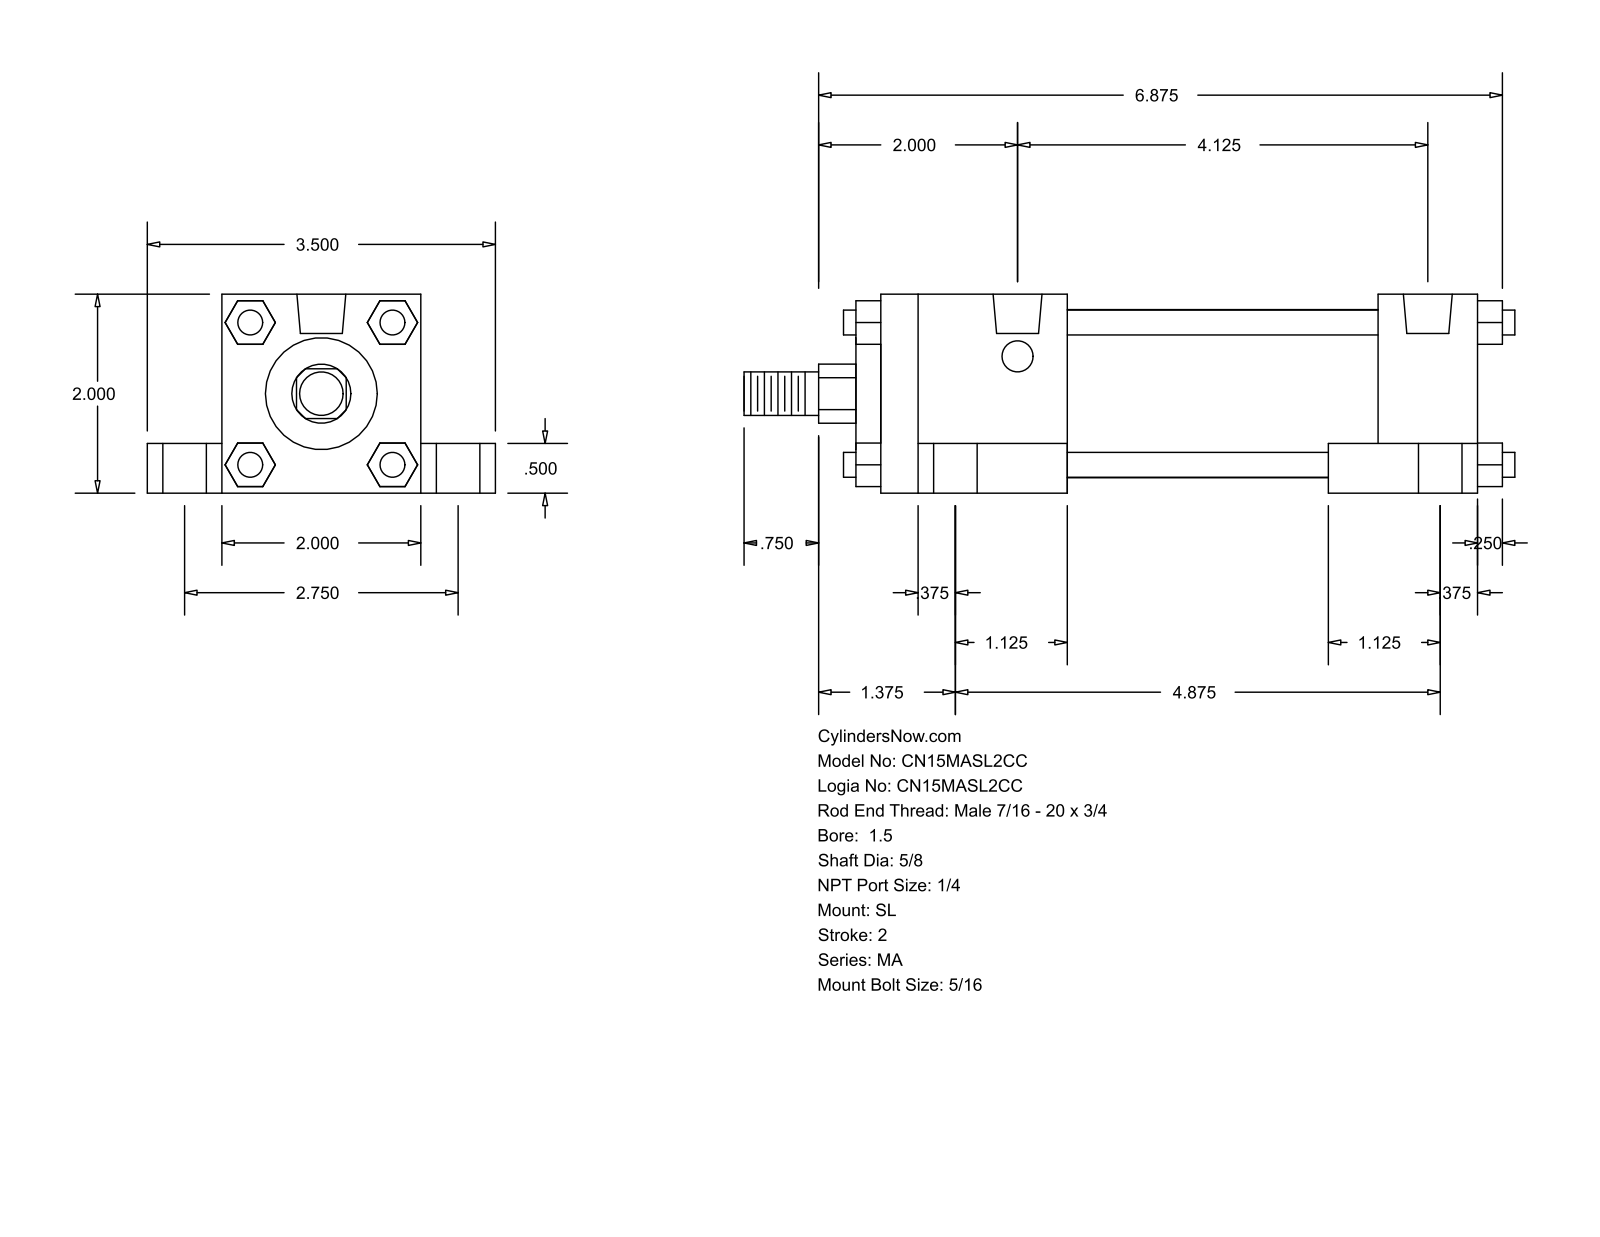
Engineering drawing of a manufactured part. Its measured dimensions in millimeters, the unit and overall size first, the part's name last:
Units: millimetres
Overall size (bounding box): 196.85 × 88.9 × 50.8
Round holes (diameter × count): ⌀7.94 ×4, ⌀11.11 ×4, ⌀17.46 ×4, ⌀12.49 ×2
Round bosses / shafts (diameter × count): ⌀6.35 ×4, ⌀42.93 ×1, ⌀28.57 ×1, ⌀15.88 ×1, ⌀11.11 ×1
Partial cylindrical surfaces — rounded edges, fillets, slot ends (radius × count): R7.54 ×1
Main face-to-face distances: 50.8, 19.05, 38.1, 152.4, 69.85, 12.7, 9.52, 25.4, 127, 47.62
Hole centre spacings: 35.06, 38.36, 69.84, 104.77, 113.46, 123.83, 125.6, 142.17
Bodies: 0 solids, 148 faces (112 planar, 36 cylindrical, 0 other)
Part name (STEP PRODUCT): MA_SL__0150_0.625
STEP written by: GSSL Pune (CONFIG_CONTROL_DESIGN)
